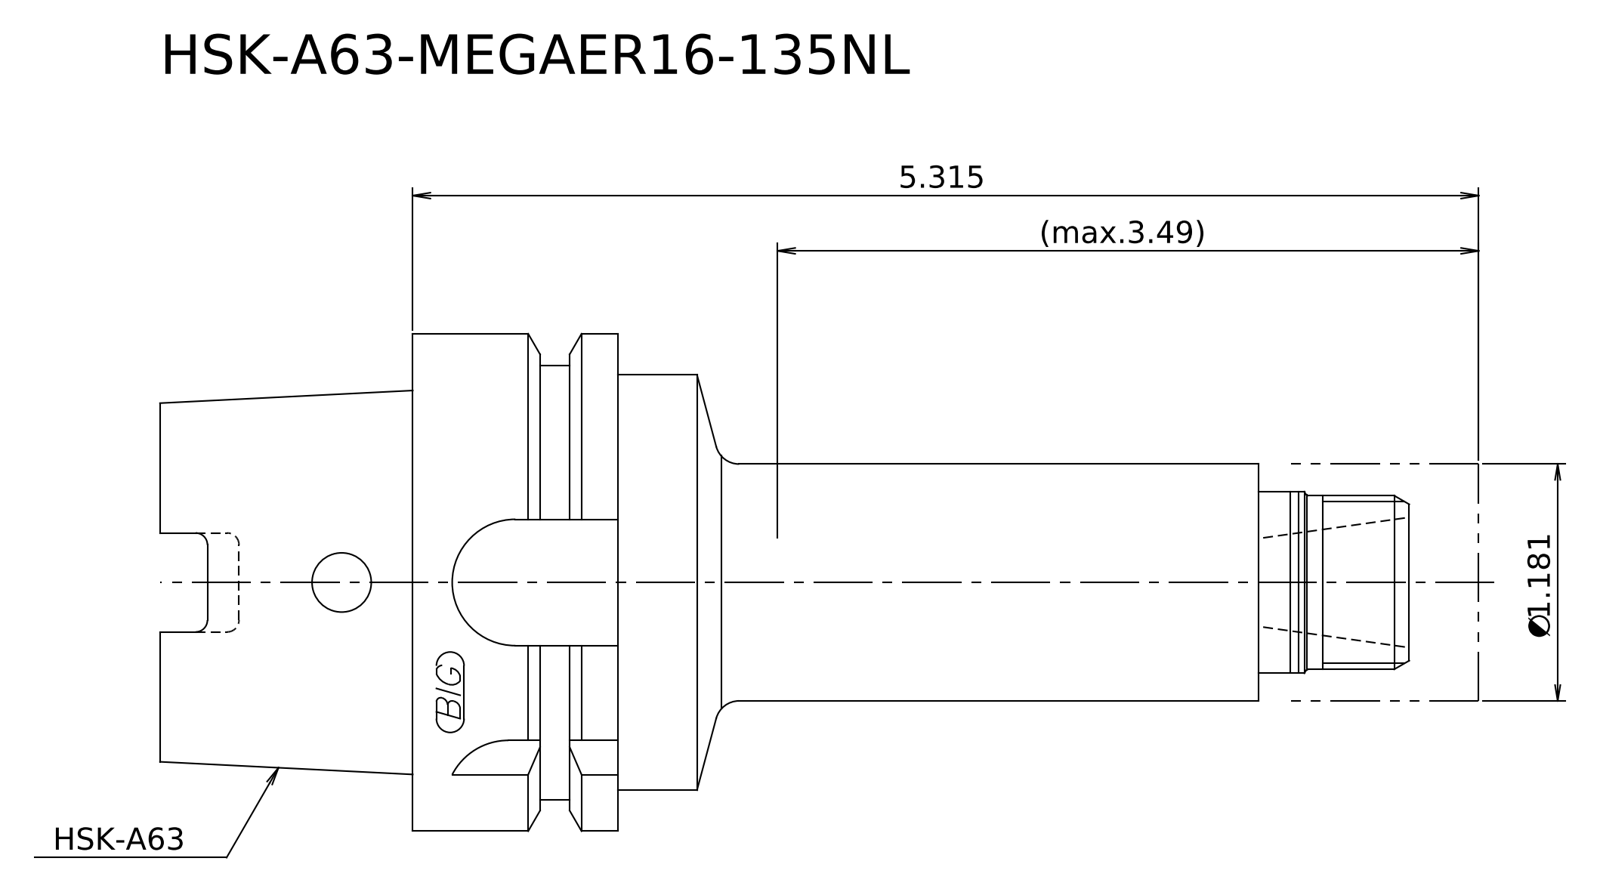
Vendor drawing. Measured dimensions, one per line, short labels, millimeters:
written by: Kubotek KeyCreator 2011 V10.0.2 (22737) (automotive_design)
unit: mm
bodies: 2 solids, 23 faces (9 planar, 8 cylindrical, 6 other)
size: 167 × 63 × 63
volume: 233 737 mm³; area: 29 865 mm²
bosses: 1× ⌀63, 1× ⌀55, 1× ⌀52.6, 1× ⌀30, 1× ⌀23, 1× ⌀22
face distances: 32, 26, 58, 84, 110, 142, 25, 109, 135, 167
